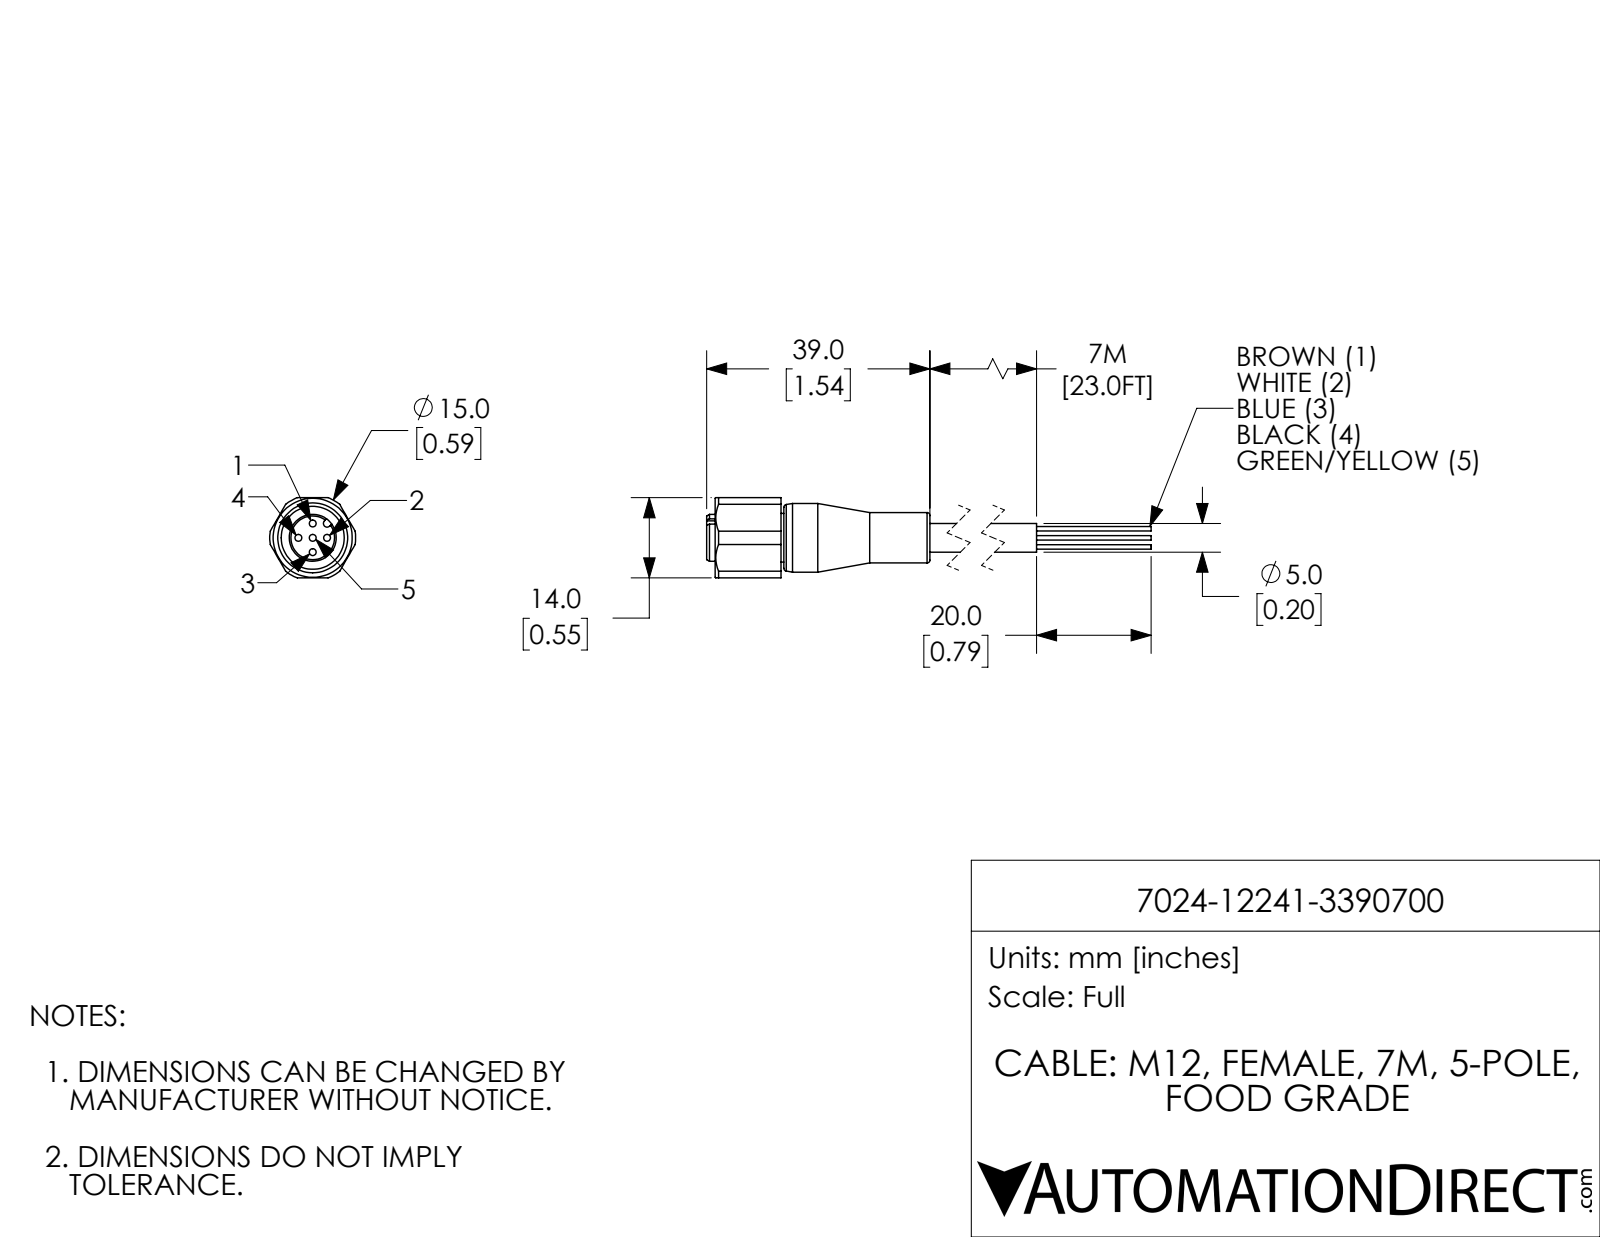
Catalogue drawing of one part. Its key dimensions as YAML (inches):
part_name: "7024-12241-3390700"
step_written_by: "SolidWorks 2018 (AUTOMOTIVE_DESIGN)"
units: inches
bodies: {solids: 1, faces: 80, planar: 26, cylindrical: 39, other: 15}
overall_size: [3.063, 0.591, 0.551]
volume: 0.252
surface_area: 4.458
round_holes:
  - {diameter: 0.047, count: 5}
  - {diameter: 0.433, count: 1}
round_bosses_or_shafts:
  - {diameter: 0.03, count: 5}
  - {diameter: 0.472, count: 1}
  - {diameter: 0.346, count: 1}
  - {diameter: 0.335, count: 1}
  - {diameter: 0.323, count: 1}
  - {diameter: 0.197, count: 1}
partial_cylinders:
  - {radius: 0.026, count: 1}
  - {radius: 0.295, count: 1}
face_to_face_distances: [0.551, 0.157, 0.354, 0.512, 0.059, 0.295, 0.453, 0.531, 0.472, 0.177]
hole_center_spacings: [0.098, 0.139, 0.197]
